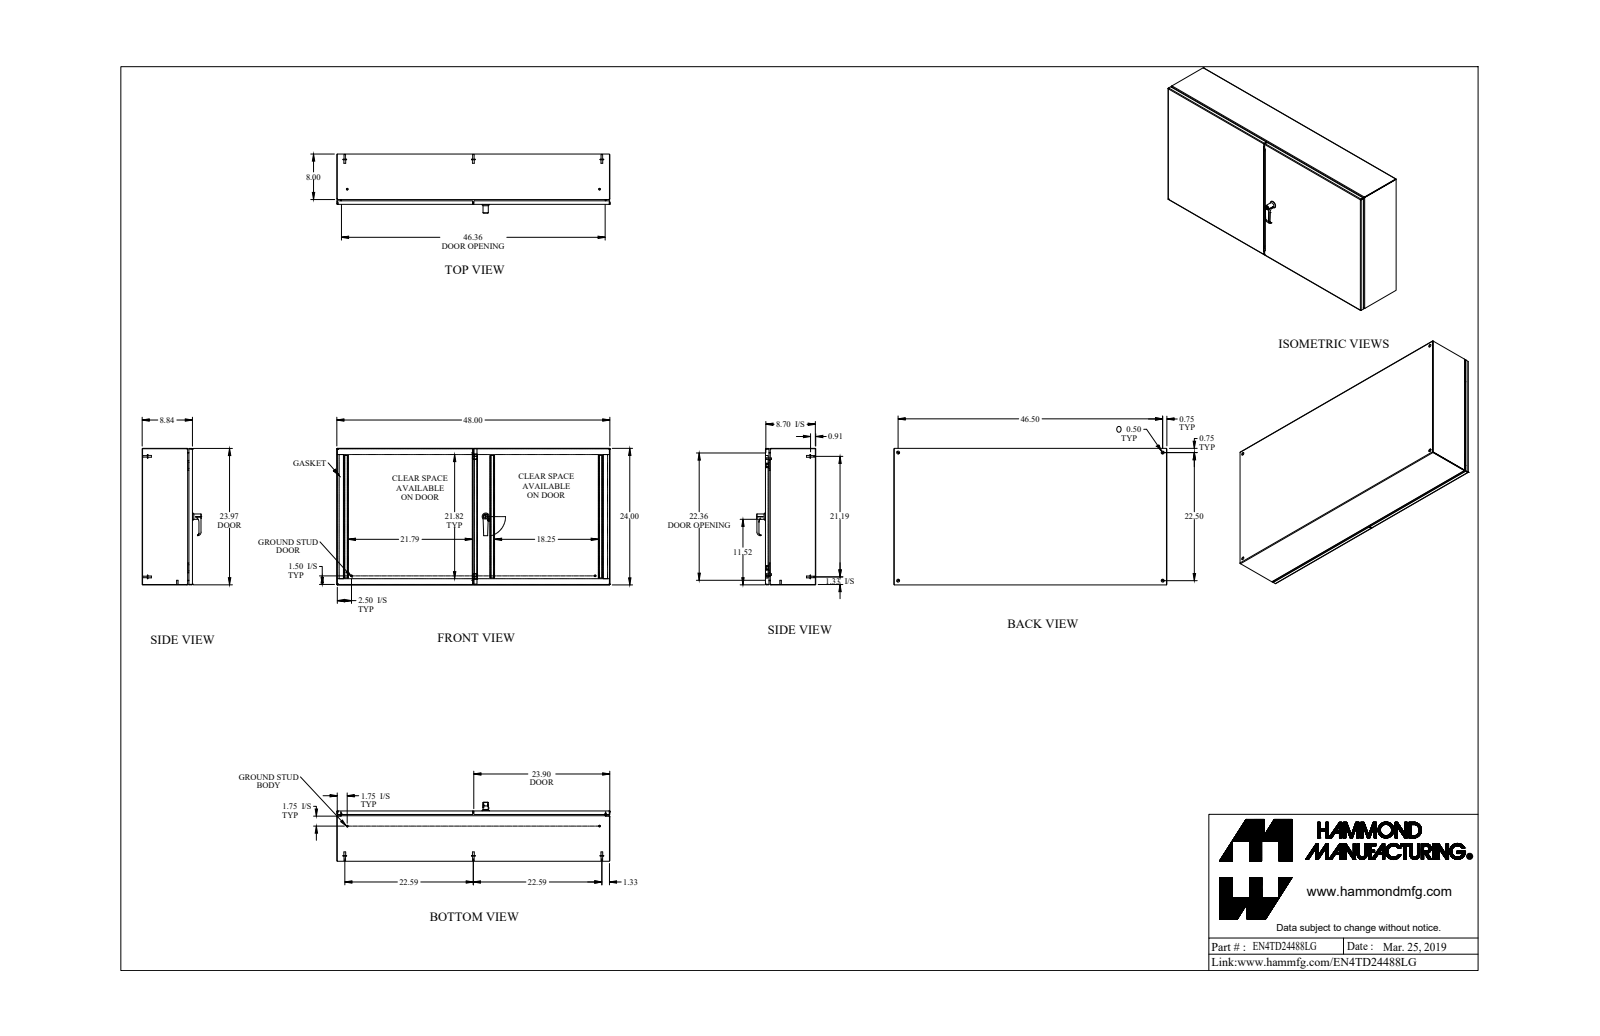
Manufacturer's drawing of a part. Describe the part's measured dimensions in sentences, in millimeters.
The part is named "EN4TD24488LG". Its 3-D file was written by "SolidWorks 2018 (AUTOMOTIVE_DESIGN)". It is 77 solids with 1935 faces: 883 planar, 714 cylindrical and 338 other. Overall it measures 1219.2 by 609.6 by 263.4 millimeters. Its volume is 5 244 000 cubic millimeters and its surface area 5 355 000 square millimeters. Round holes: 5 of diameter 5, 4 of diameter 4.5, 4 of diameter 6.7, 4 of diameter 12.7, 3 of diameter 6.1, 3 of diameter 6.1, 2 of diameter 4.4, 2 of diameter 6.4, 2 of diameter 6.5, 2 of diameter 6.6, 2 of diameter 8, 2 of diameter 10. Round bosses or shafts: 12 of diameter 6.4, 8 of diameter 8, 6 of diameter 15.9, 6 of diameter 6.9, 4 of diameter 13, 4 of diameter 9.5, 4 of diameter 7.1, 4 of diameter 4. Partial cylindrical surfaces (rounded edges, fillets, slot ends): 26 of radius 0.9, 26 of radius 2.7, 20 of radius 2.4, 18 of radius 1.1, 18 of radius 1.6, 18 of radius 2.1, 16 of radius 0.5, 15 of radius 0.4. The main face-to-face distances are 1.8, 222.8, 220.9, 224.6, 607.8, 605.9, 1217.4, 609.6, 1215.5, 1219.2. The hole center spacings are 20, 258.8, 528.3, 571.5, 607, 654.1, 706, 1181.1.
